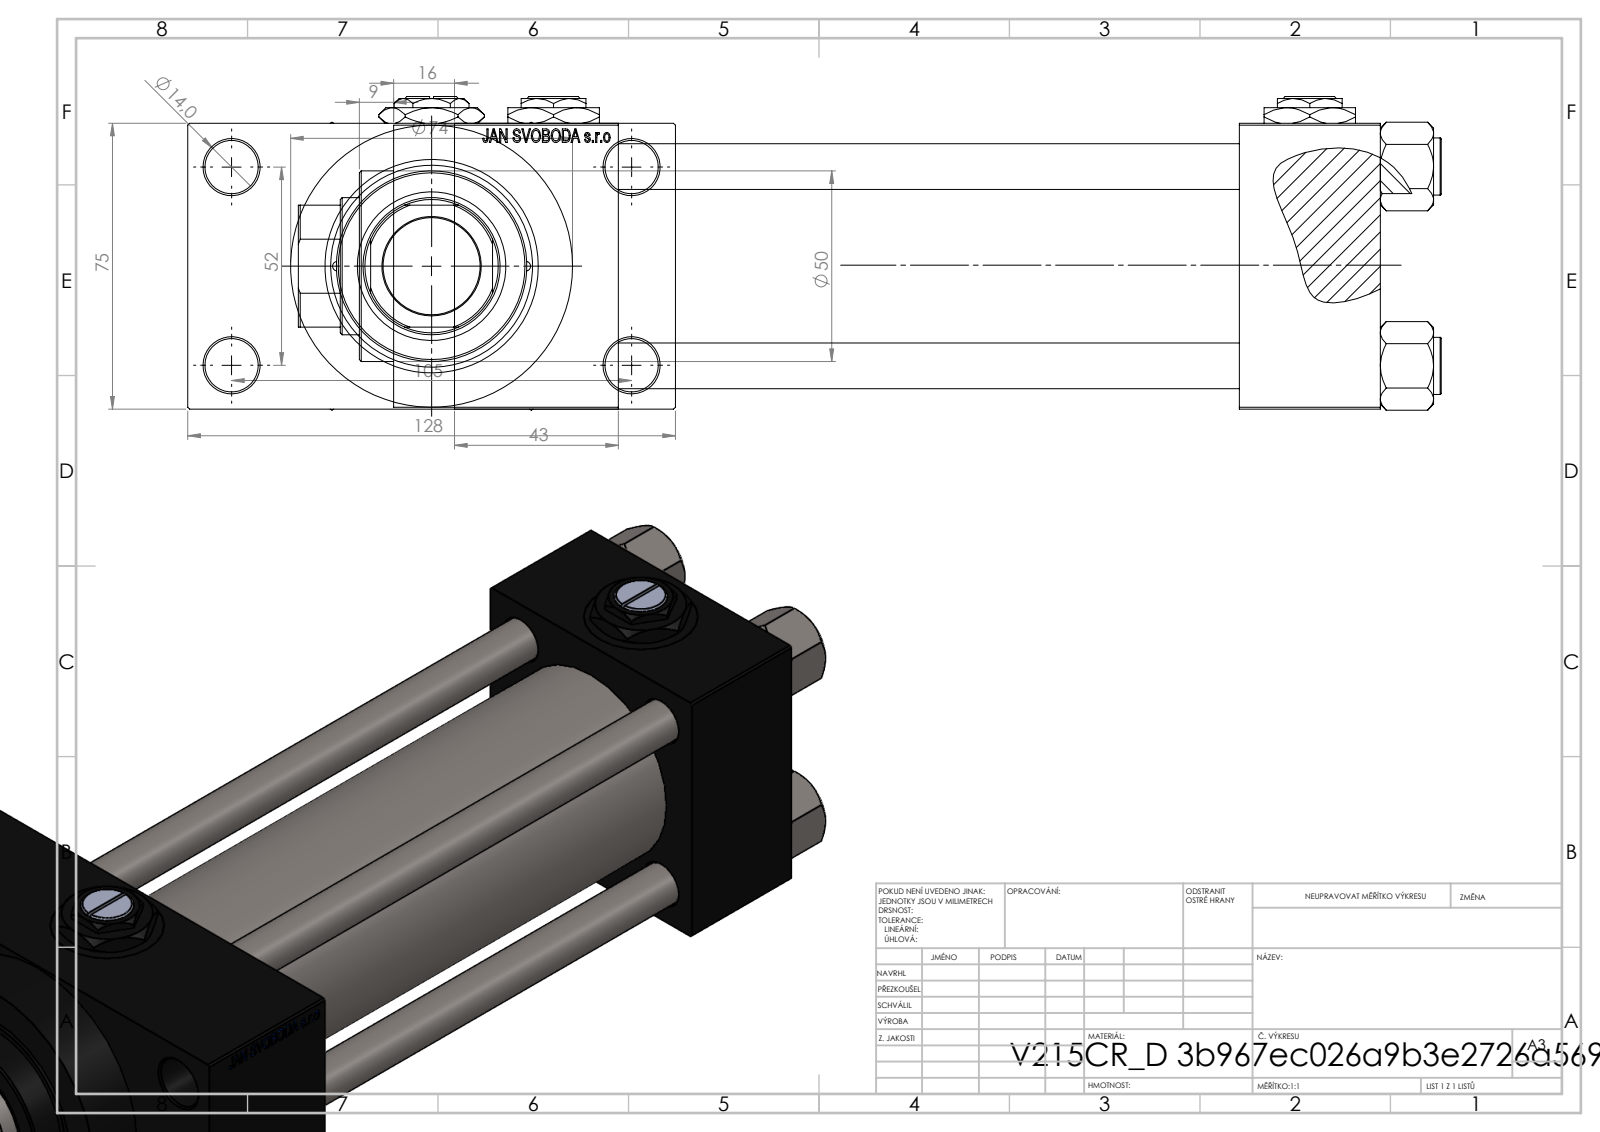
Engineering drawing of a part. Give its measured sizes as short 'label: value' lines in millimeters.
name: V215_VC_A; V215CR_VCP_D; V215CR_D_TYCINKA; NUT_M5_D (+2 more)
written by: SolidWorks 2019 (CONFIG_CONTROL_DESIGN)
unit: mm
bodies: 13 solids, 1214 faces (549 planar, 103 cylindrical, 562 other)
size: 300 × 128 × 82.27
volume: 1 020 000 mm³; area: 242 388 mm²
holes: 4× ⌀12, 4× ⌀14, 4× ⌀20.96, 4× ⌀30, 3× ⌀7, 2× ⌀2.5, 1× ⌀25.5, 1× ⌀36, 1× ⌀39, 1× ⌀41, 1× ⌀53
bosses: 4× ⌀15, 1× ⌀74, 1× ⌀56, 1× ⌀50
rounds: 1× R17.5
face distances: 75, 163, 37, 200, 26.5, 243, 43, 206, 101.5, 16
hole spacings: 26.19, 26.35, 36.98, 38.03, 52.3, 57.22, 58.43, 58.59
